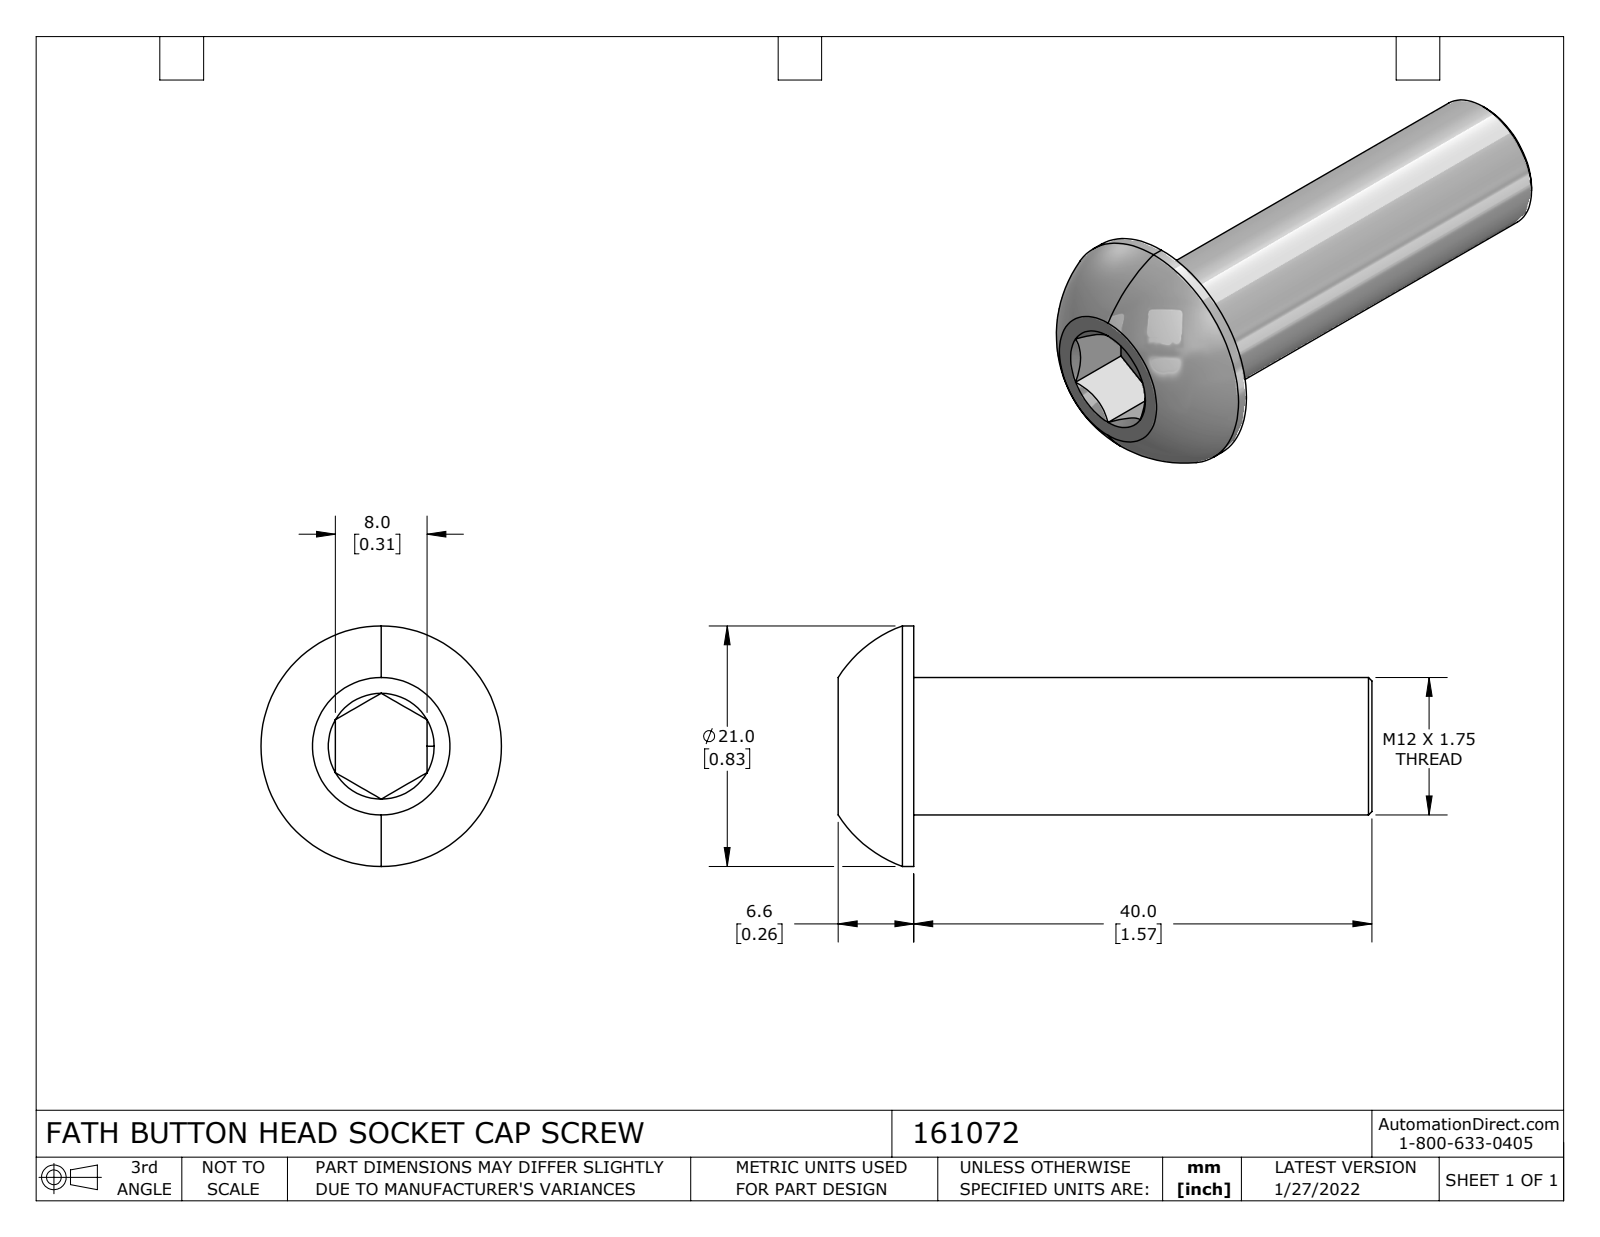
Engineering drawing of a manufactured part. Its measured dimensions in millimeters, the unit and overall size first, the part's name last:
Units: millimetres
Overall size (bounding box): 46.6 × 21 × 21
Round bosses / shafts (diameter × count): ⌀21 ×1, ⌀12 ×1
Main face-to-face distances: 40, 8, 41, 1, 46.6, 6.6, 5.6
Volume: 5 933 mm³ · Surface area: 2 569 mm²
Bodies: 1 solid, 25 faces (10 planar, 4 cylindrical, 11 other)
Part name (STEP PRODUCT): 161072
STEP written by: SolidWorks 2021 (CONFIG_CONTROL_DESIGN)
